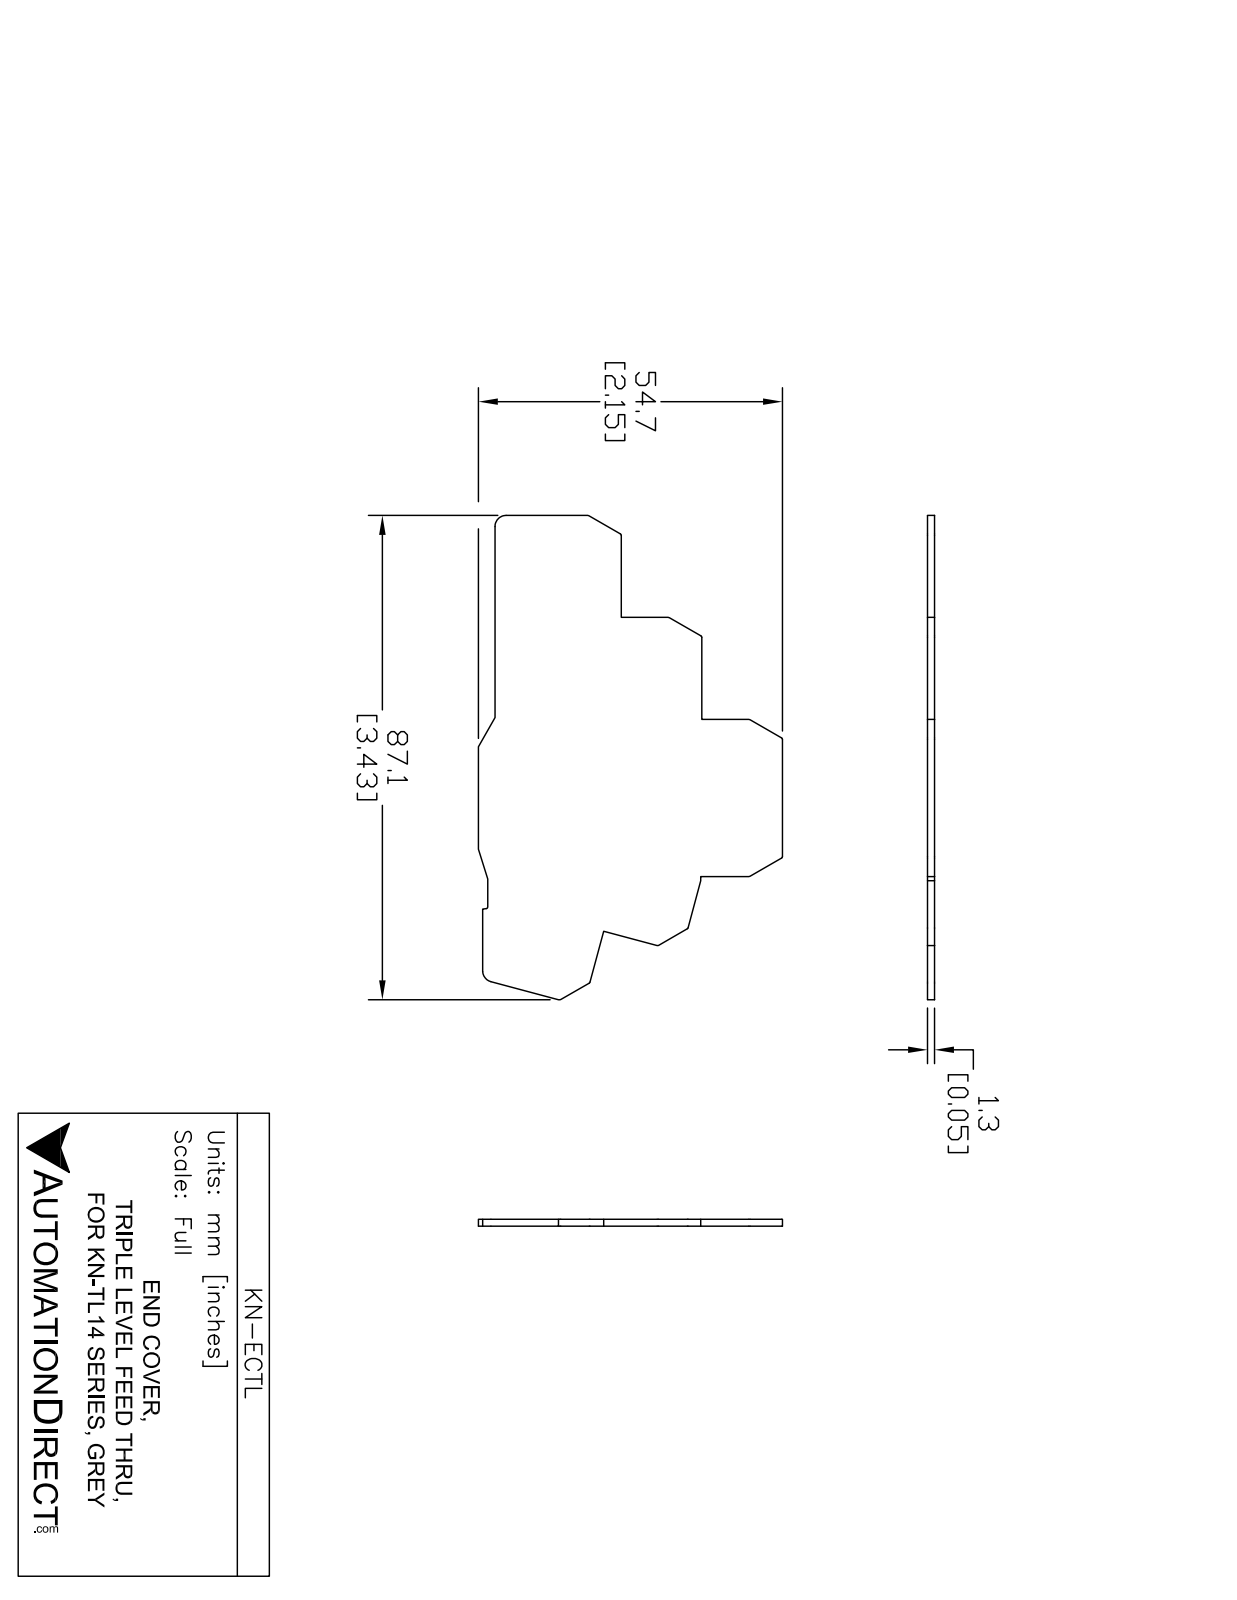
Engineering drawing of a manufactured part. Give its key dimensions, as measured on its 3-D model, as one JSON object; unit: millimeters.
{"part_name": "KN-ECTL", "step_written_by": "SolidWorks 2014 (AUTOMOTIVE_DESIGN)", "units": "millimeters", "bodies": {"solids": 1, "faces": 43, "planar": 28, "cylindrical": 15, "other": 0}, "overall_size": [87.15, 54.7, 1.25], "volume_mm3": 3998, "surface_area_mm2": 6723, "partial_cylinders_radius": [[0.3, 9], [0.5, 3], [2, 2], [0.45, 1]], "face_to_face_distances": [1.24, 14.5, 51.71, 2.99, 54.7, 40.2, 37.21, 25.7, 22.71, 29]}
